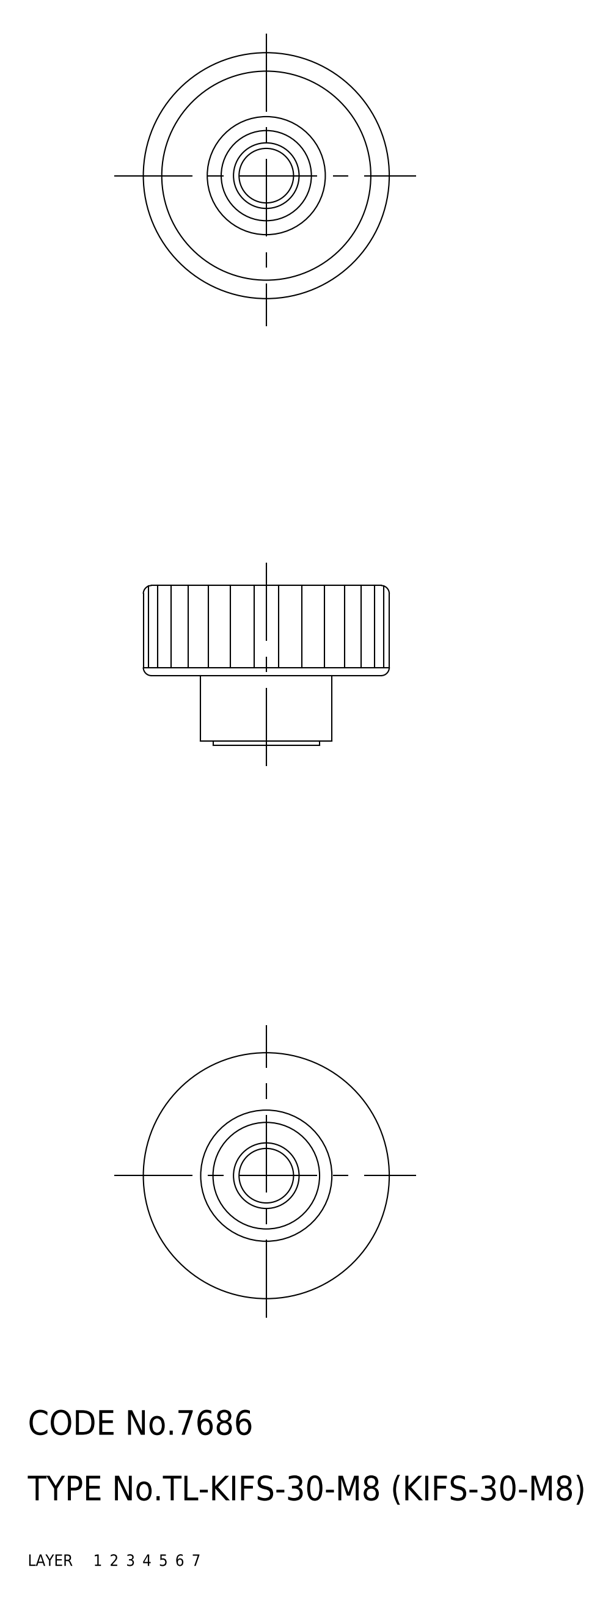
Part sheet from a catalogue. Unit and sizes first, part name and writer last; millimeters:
Units: millimetres
Overall size (bounding box): 30 × 30 × 19.5
Volume: 4 389 mm³ · Surface area: 4 365 mm²
Bodies: 2 solids, 28 faces (0 planar, 0 cylindrical, 28 other)
Part name (STEP PRODUCT): screw; knob; KIFS_30_M8_3852_36
STEP written by: CADfix (AUTOMOTIVE_DESIGN)
